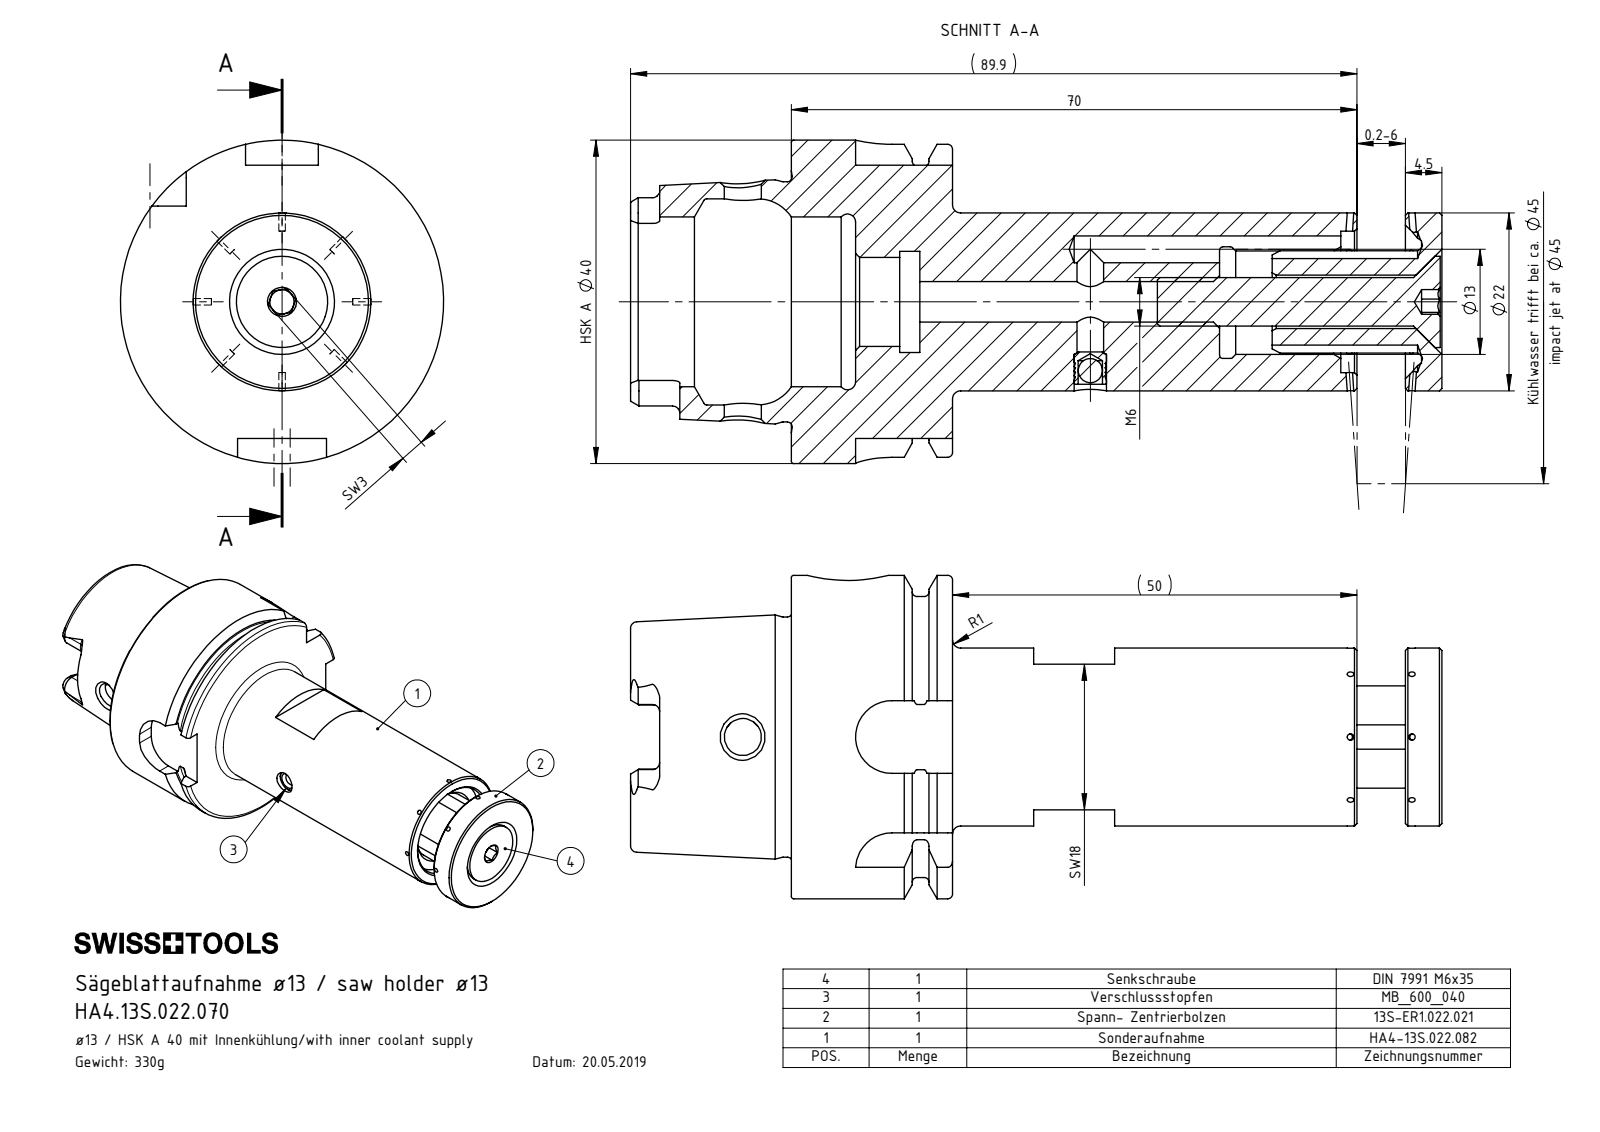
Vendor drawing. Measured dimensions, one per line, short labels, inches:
name: KVT_MB_600_040; DIN 7991 - M6x35; HA4.13S.022.070; HA4-13S.022.070_A_Fertigbearbeitung (+1 more)
written by: SolidWorks 2017 (AUTOMOTIVE_DESIGN)
unit: in
bodies: 5 solids, 235 faces (72 planar, 74 cylindrical, 89 other)
size: 3.953 × 1.575 × 1.575
volume: 2.627 in³; area: 27.71 in²
holes: 16× ⌀0.031, 2× ⌀0.13, 1× ⌀0.118, 1× ⌀0.181, 1× ⌀0.197, 1× ⌀0.26, 1× ⌀0.394, 1× ⌀0.433, 1× ⌀0.492, 1× ⌀0.551, 1× ⌀0.689, 1× ⌀0.827
bosses: 1× ⌀1.575, 1× ⌀1.368, 1× ⌀1.17, 1× ⌀0.866, 1× ⌀0.512, 1× ⌀0.445, 1× ⌀0.236, 1× ⌀0.157
rounds: 6× R0.035, 4× R0.065, 4× R0.074, 4× R0.177
face distances: 0.785, 0.313, 3.169, 2.384, 0.472, 2.856, 0.413, 0.783, 1.096, 1.569
hole spacings: 0.359, 0.256, 1.693
